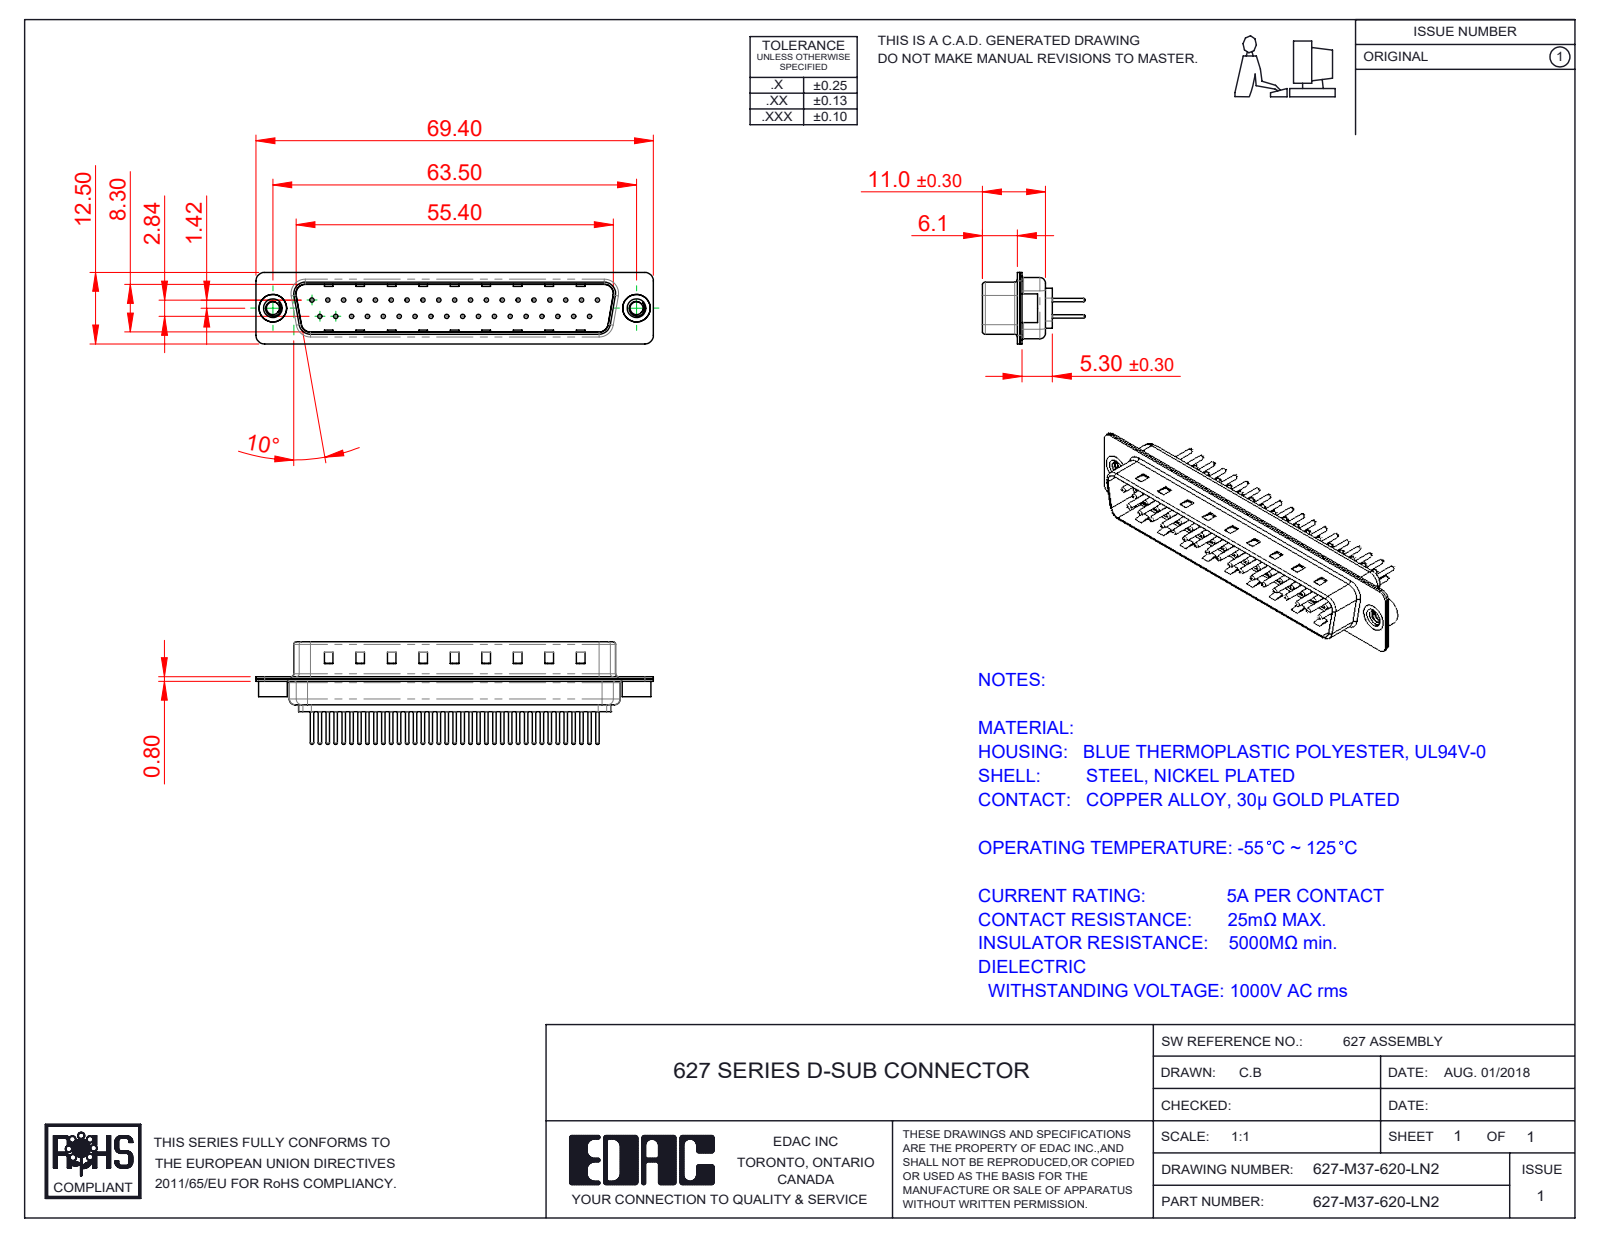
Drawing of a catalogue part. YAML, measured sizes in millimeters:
part_name: "627M Shell Front_37 Contacts; 627M Housing_37 Contacts; 627M 4-40 Threaded Rivet; 627-M37-620-LN2 (+3 more)"
step_written_by: "SolidWorks 2020 (CONFIG_CONTROL_DESIGN)"
units: millimeters
bodies: {solids: 42, faces: 1781, planar: 462, cylindrical: 659, other: 660}
overall_size: [69.4, 17.9, 12.5]
volume: 3768
surface_area: 9269
round_holes:
  - {diameter: 0.75, count: 37}
  - {diameter: 1.6, count: 37}
  - {diameter: 2, count: 37}
  - {diameter: 2.26, count: 2}
  - {diameter: 4, count: 2}
  - {diameter: 4.8, count: 2}
round_bosses_or_shafts:
  - {diameter: 1.5, count: 37}
  - {diameter: 0.6, count: 37}
  - {diameter: 5, count: 2}
  - {diameter: 4.9, count: 2}
partial_cylinders:
  - {radius: 1.5, count: 16}
  - {radius: 2, count: 12}
  - {radius: 0.5, count: 8}
  - {radius: 1.6, count: 8}
  - {radius: 0.25, count: 4}
  - {radius: 0.6, count: 4}
  - {radius: 0.65, count: 4}
  - {radius: 0.9, count: 4}
face_to_face_distances: [0.4, 0.8, 9.5, 9.1, 8.7, 9.9, 1.2, 5.7, 0.75, 0.35]
hole_center_spacings: [2.77, 5.54, 3.16, 8.31, 11.08, 13.85, 16.62, 19.39]
